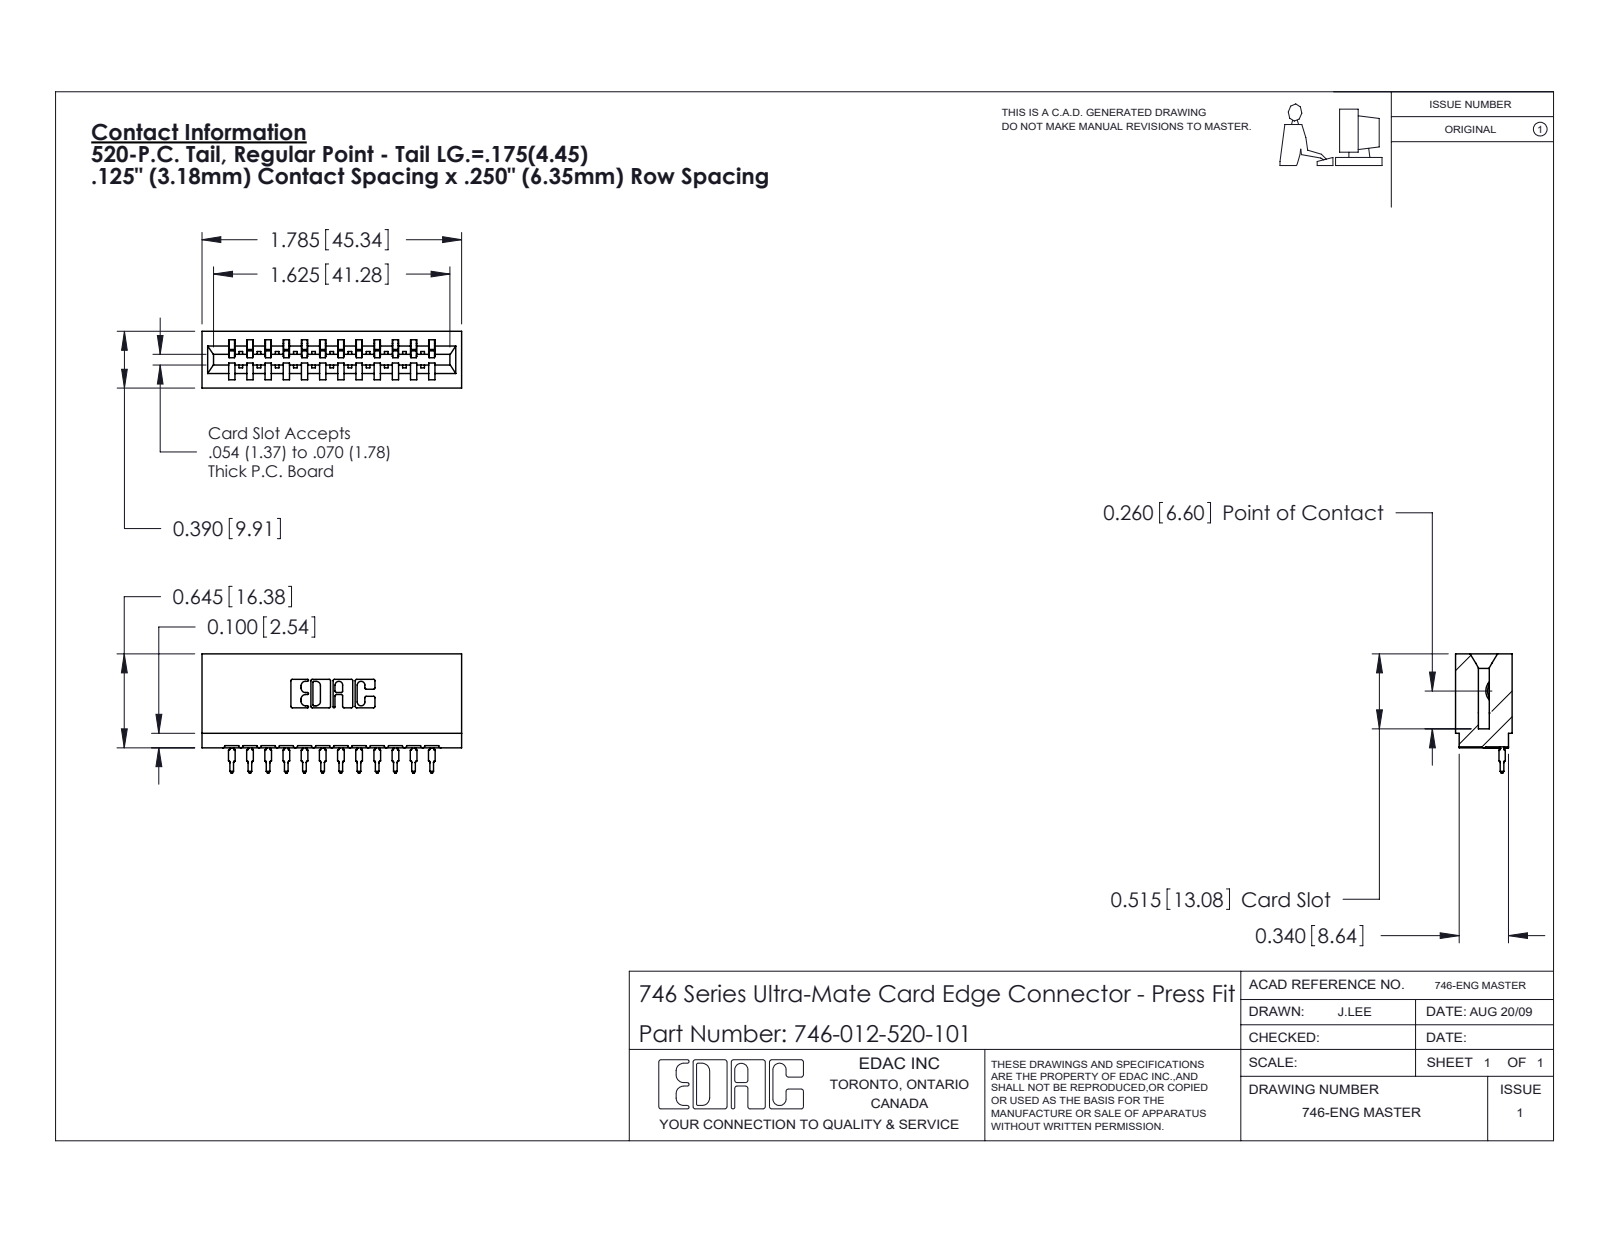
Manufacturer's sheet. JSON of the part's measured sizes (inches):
{"part_name": "746 Part_.515 Slot Depth - 01; 746-292-001_520; 746-012-520-101", "step_written_by": "SolidWorks 2020 (CONFIG_CONTROL_DESIGN)", "units": "inches", "bodies": {"solids": 13, "faces": 1393, "planar": 811, "cylindrical": 270, "other": 312}, "overall_size": [1.785, 0.819, 0.39], "volume_in3": 0.3, "surface_area_in2": 10.4, "partial_cylinders_radius": [[0.021, 24], [0.01, 22], [0.015, 13], [0.007, 6], [0.031, 6], [0.005, 4], [0.011, 4], [0.026, 3]], "face_to_face_distances": [0.25, 0.333, 0.5, 0.057, 0.125, 0.125, 0.39, 0.042, 0.208, 0.292]}
